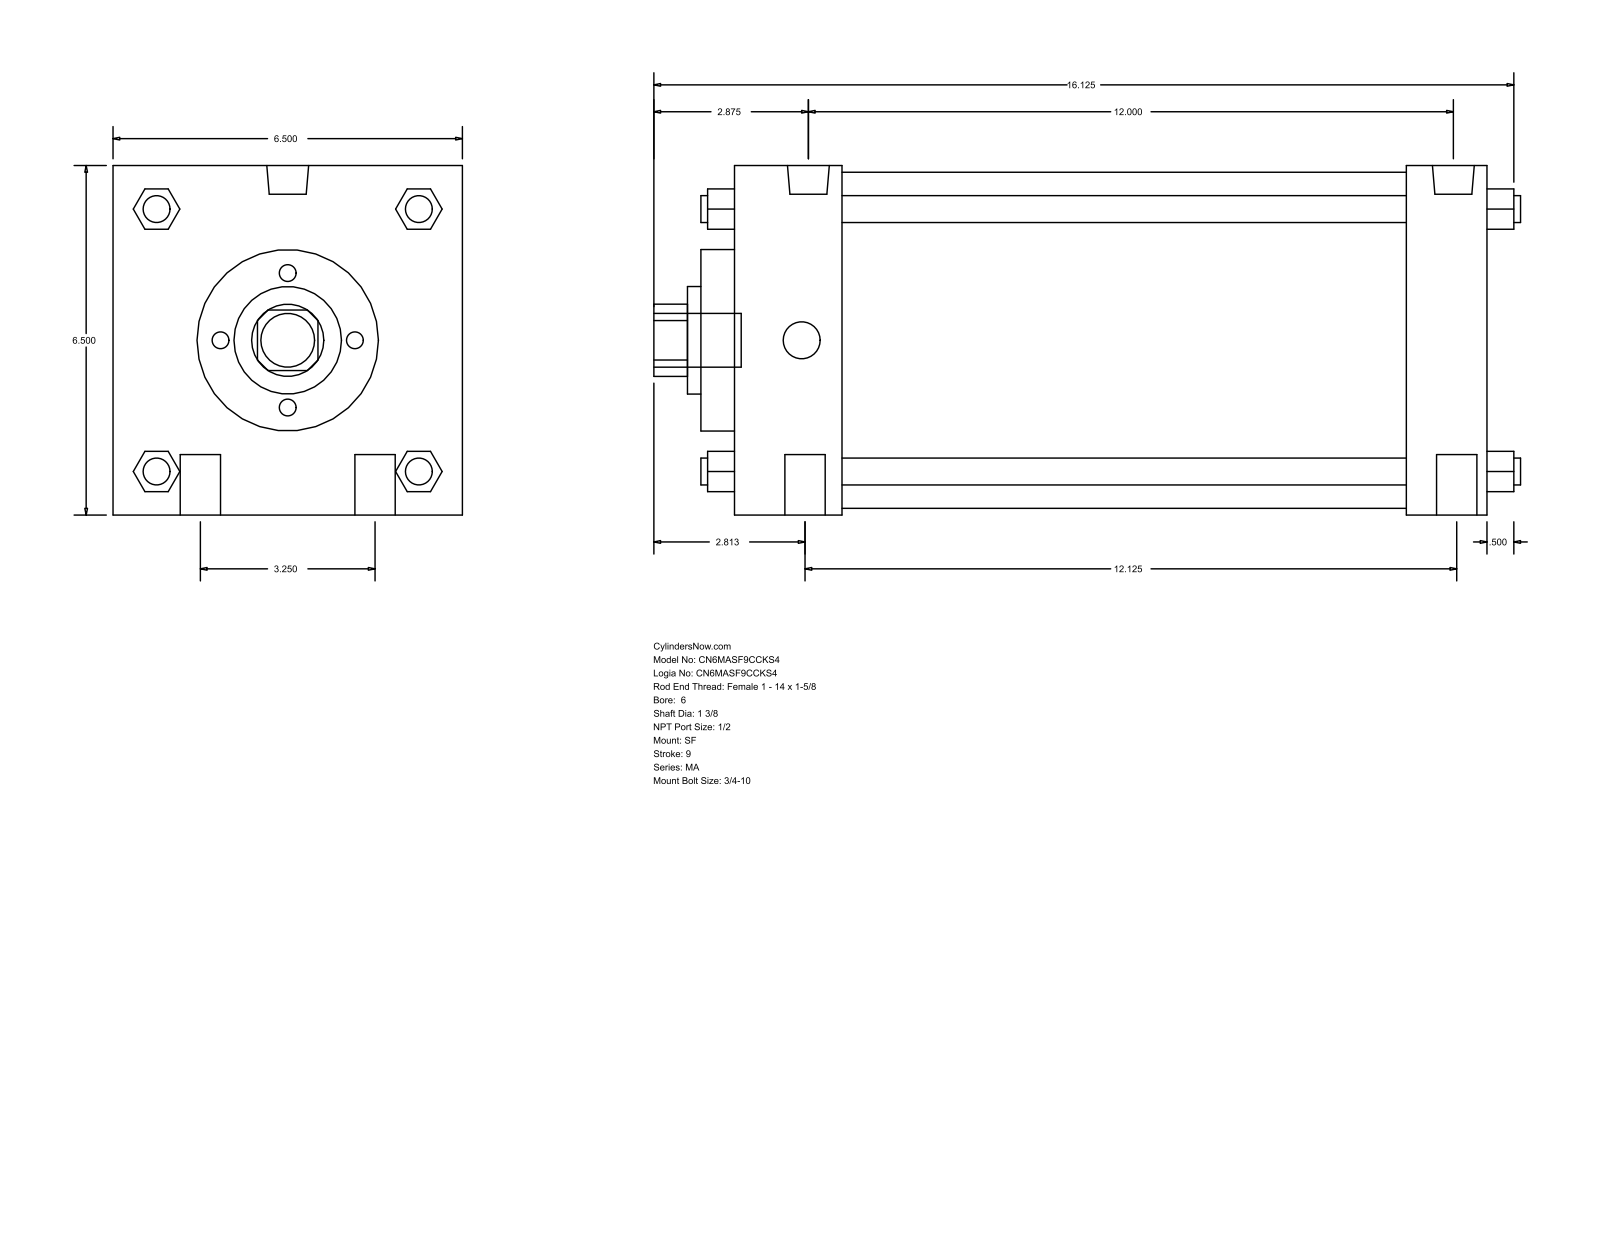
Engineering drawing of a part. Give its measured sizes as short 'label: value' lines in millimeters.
name: MA_SF__0600_1.375
written by: GSSL Pune (CONFIG_CONTROL_DESIGN)
unit: mm
bodies: 0 solids, 126 faces (95 planar, 31 cylindrical, 0 other)
size: 409.57 × 165.1 × 165.1
holes: 1× ⌀34.92, 1× ⌀50.8, 1× ⌀85.72, 1× ⌀158.75
bosses: 4× ⌀19.05, 4× ⌀12.7, 2× ⌀19.77, 2× ⌀17.46, 1× ⌀25.4
rounds: 1× R17.06
face distances: 165.1, 355.6, 317.5, 50.8, 38.1, 266.7, 304.8, 15.87, 371.47, 66.67
